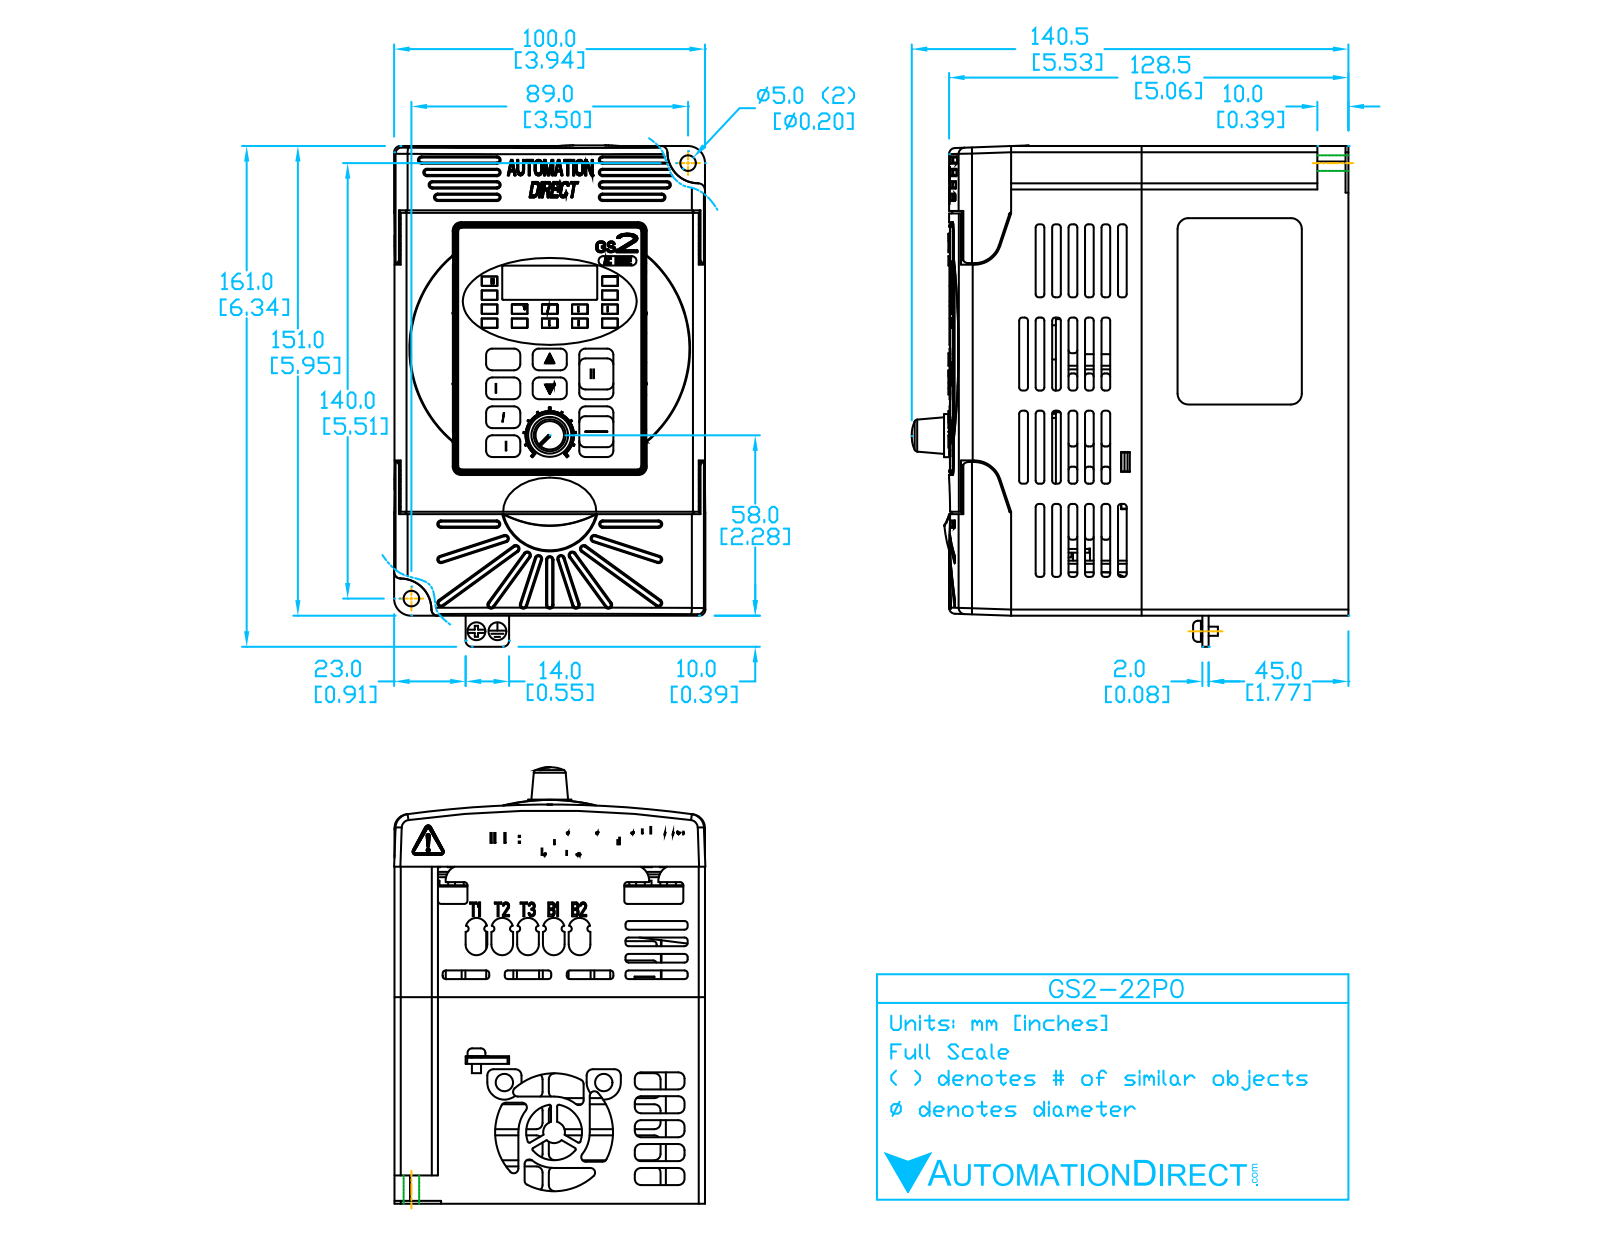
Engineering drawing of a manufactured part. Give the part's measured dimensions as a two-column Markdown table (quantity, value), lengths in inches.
| quantity | value |
| --- | --- |
| part name | GS2-22P0 |
| STEP written by | SolidWorks 2015 (AUTOMOTIVE_DESIGN) |
| units | inches |
| bodies | 1 solid, 753 faces (324 planar, 220 cylindrical, 209 other) |
| overall size | 6.345 × 5.495 × 3.94 |
| volume | 112.9 in³ |
| surface area | 196.7 in² |
| round holes (diameter × count) | 0.2 × 2, 0.7 × 1, 1.46 × 1 |
| round bosses / shafts (diameter × count) | 0.545 × 1, 0.22 × 1, 0.15 × 1 |
| partial cylindrical surfaces (radius × count) | 0.04 × 40, 0.06 × 16, 0.03 × 14, 0.125 × 10, 0.03 × 8, 0.045 × 6, 0.2 × 6, 0.1 × 4 |
| main face-to-face distances | 3.94, 5.95, 4.256, 4.266, 0.015, 5.935, 0.03, 0.761, 3.179, 0.03 |
| hole center spacings | 6.528 |
